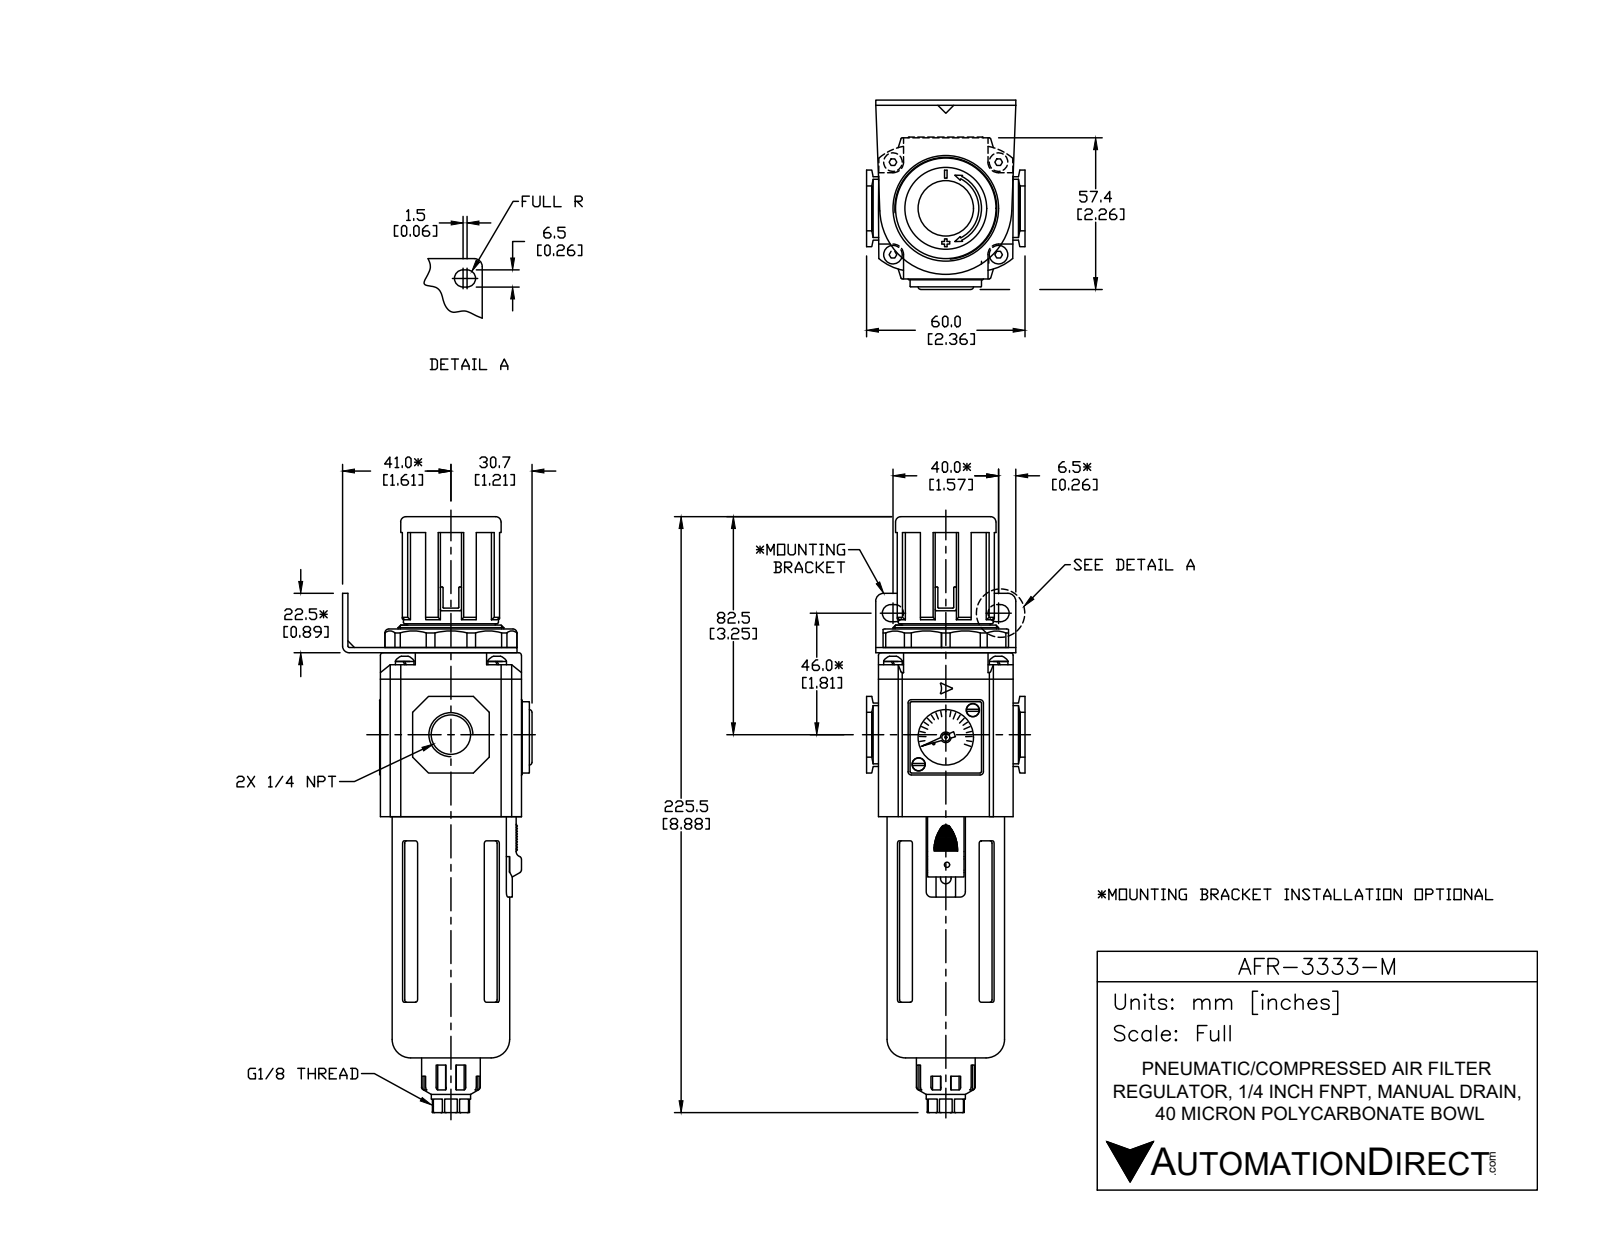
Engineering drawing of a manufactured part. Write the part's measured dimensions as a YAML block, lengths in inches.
part_name: "AFR-3333-M"
step_written_by: "SolidWorks 2015 (CONFIG_CONTROL_DESIGN)"
units: inches
bodies: {solids: 16, faces: 606, planar: 370, cylindrical: 172, other: 64}
overall_size: [8.882, 2.835, 2.362]
volume: 16.68
surface_area: 108.8
round_holes:
  - {diameter: 0.118, count: 6}
  - {diameter: 0.079, count: 1}
  - {diameter: 0.244, count: 1}
  - {diameter: 0.562, count: 1}
  - {diameter: 0.63, count: 1}
  - {diameter: 0.827, count: 1}
  - {diameter: 1.181, count: 1}
  - {diameter: 1.26, count: 1}
  - {diameter: 1.386, count: 1}
round_bosses_or_shafts:
  - {diameter: 0.217, count: 4}
  - {diameter: 0.106, count: 2}
  - {diameter: 1.732, count: 1}
  - {diameter: 1.575, count: 1}
  - {diameter: 1.496, count: 1}
  - {diameter: 1.417, count: 1}
  - {diameter: 1.319, count: 1}
  - {diameter: 0.806, count: 1}
partial_cylinders:
  - {radius: 0.087, count: 18}
  - {radius: 0.039, count: 12}
  - {radius: 0.047, count: 10}
  - {radius: 0.02, count: 8}
  - {radius: 0.374, count: 8}
  - {radius: 0.128, count: 6}
  - {radius: 0.157, count: 5}
  - {radius: 0.012, count: 4}
face_to_face_distances: [0.079, 2.441, 2.52, 2.102, 2.008, 1.559, 0.039, 2.185, 2.063, 0.177]
hole_center_spacings: [1.046, 0.571, 1.378, 1.575, 2.093, 1.141]
